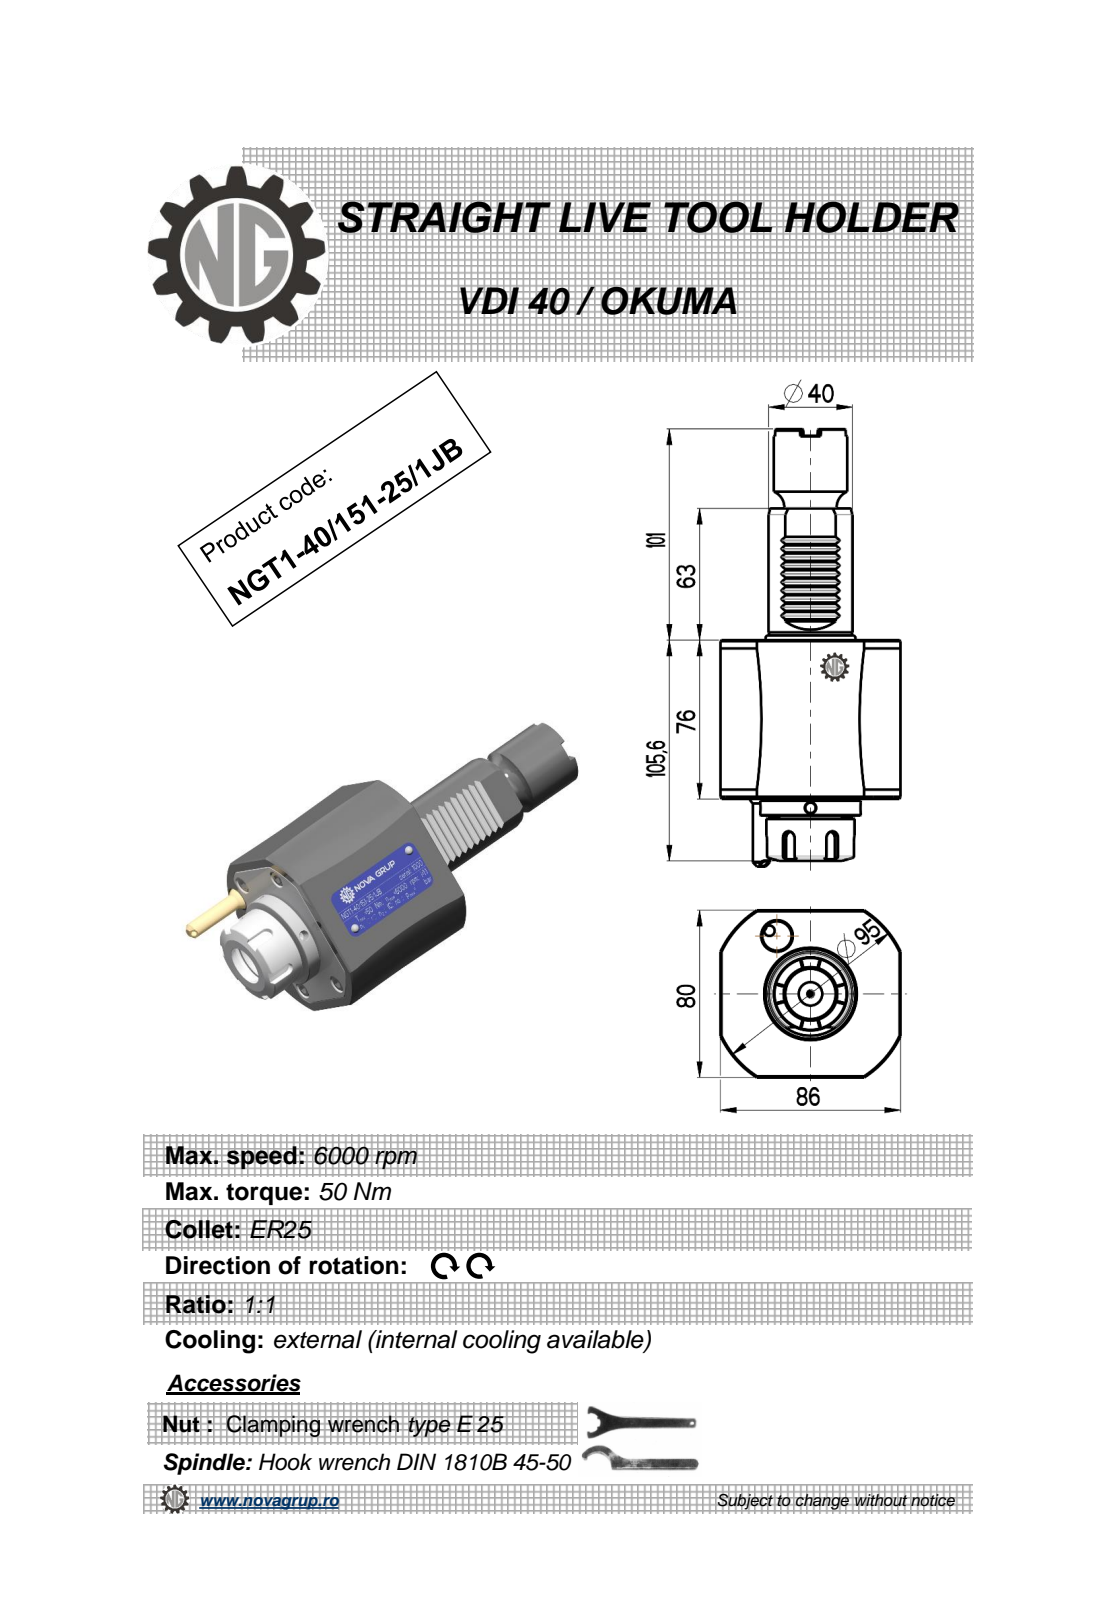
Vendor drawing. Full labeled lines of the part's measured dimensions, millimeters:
Part name (STEP PRODUCT): NGT1_40_151_25_1JB
STEP written by: PRO/ENGINEER BY PARAMETRIC TECHNOLOGY CORPORATION, 2010280 (CONFIG_CONTROL_DESIGN)
Units: millimetres
Bodies: 1 solid, 325 faces (116 planar, 66 cylindrical, 143 other)
Overall size (bounding box): 209.34 × 86 × 81.6
Volume: 621 462 mm³ · Surface area: 55 876 mm²
Round holes (diameter × count): ⌀5 ×3, ⌀3 ×1
Round bosses / shafts (diameter × count): ⌀48 ×1, ⌀42 ×1, ⌀41.5 ×1, ⌀40 ×1, ⌀35 ×1, ⌀33 ×1, ⌀25 ×1, ⌀8 ×1
Partial cylindrical surfaces — rounded edges, fillets, slot ends (radius × count): R0.3 ×10, R0.22 ×6, R3 ×5, R47.5 ×1
Main face-to-face distances: 76, 80, 86, 84, 8, 2.83, 5.66, 97.8, 173.8, 181.8
